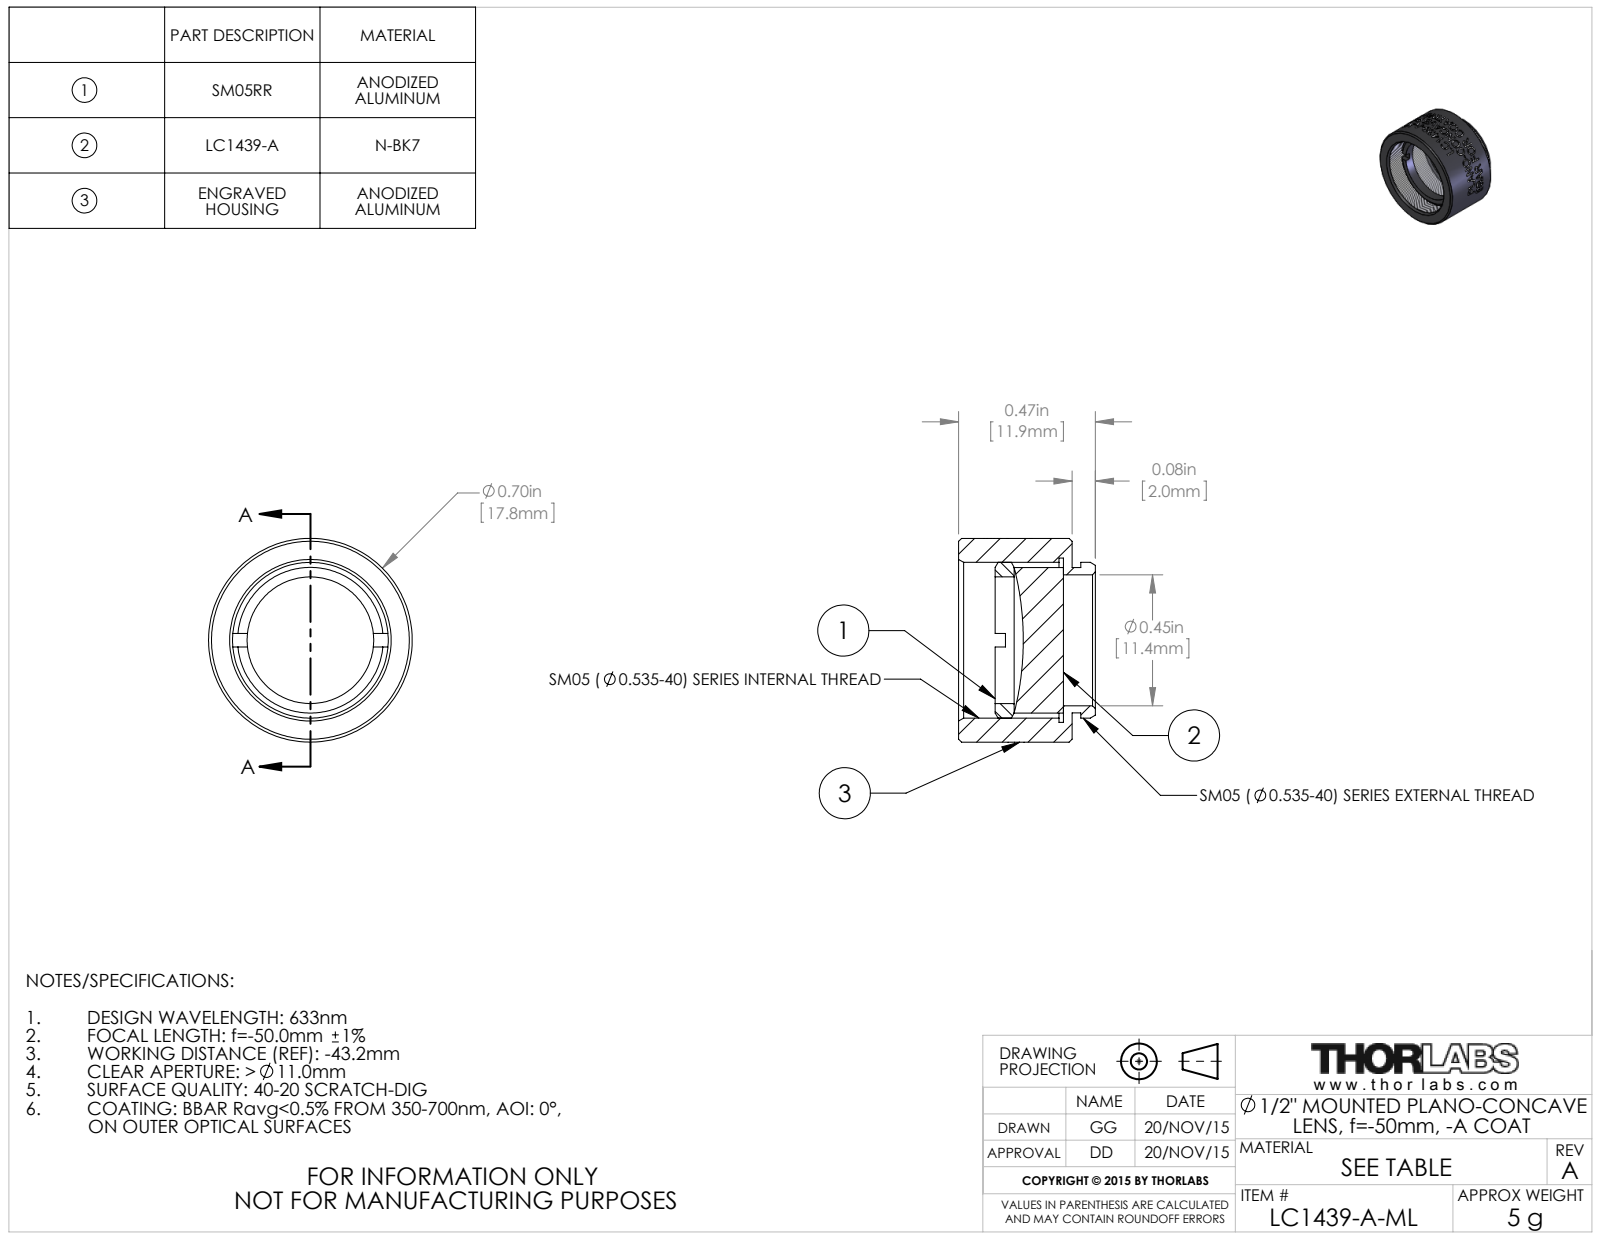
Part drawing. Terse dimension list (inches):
name: TTN045260-E0W
written by: SolidWorks 2014 (CONFIG_CONTROL_DESIGN)
unit: in
bodies: 3 solids, 149 faces (16 planar, 116 cylindrical, 17 other)
size: 0.7 × 0.7 × 0.47
volume: 0.102 in³; area: 3.242 in²
holes: 1× ⌀0.435, 1× ⌀0.45, 1× ⌀0.535, 1× ⌀0.565
bosses: 1× ⌀0.7, 1× ⌀0.535, 1× ⌀0.5, 1× ⌀0.499
face distances: 0.03, 0.39, 0.36, 0.199, 0.169, 0.191, 0.264, 0.234, 0.065, 0.126
